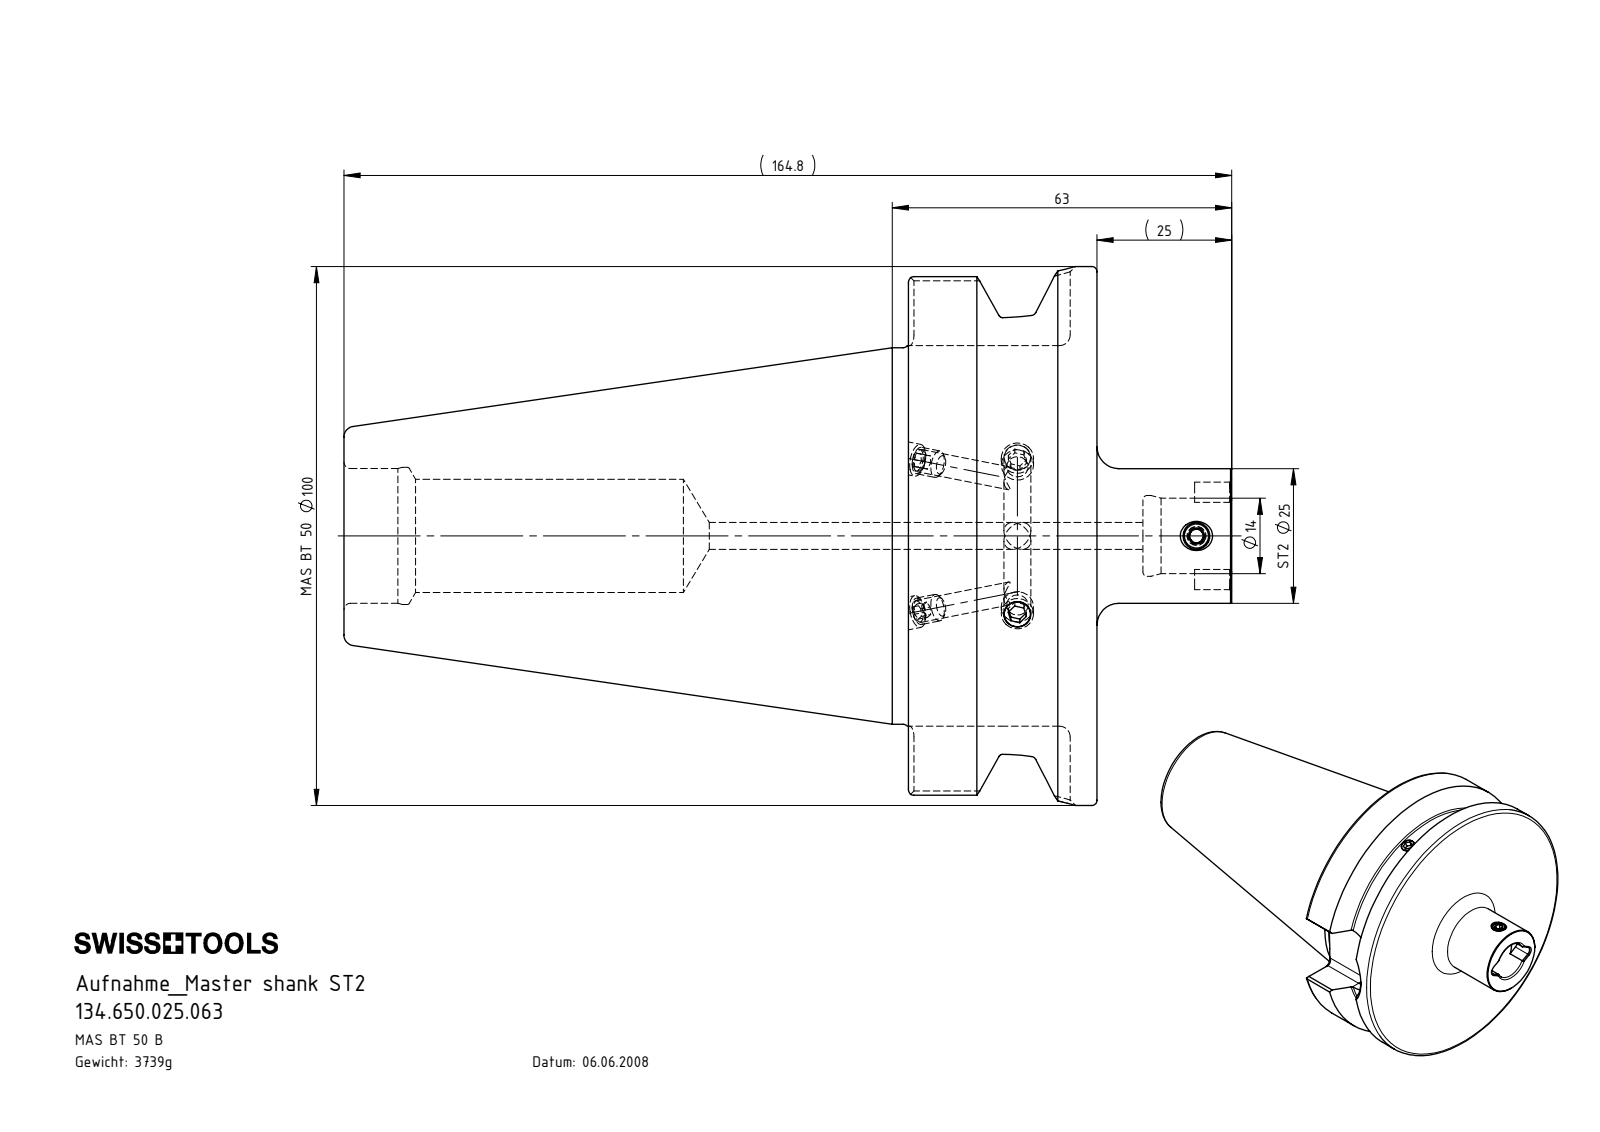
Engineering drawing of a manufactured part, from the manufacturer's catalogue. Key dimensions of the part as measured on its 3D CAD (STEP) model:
Part name (STEP PRODUCT): ST2-ER1.001.006_A; BB5-ST2.K01.063_A_mit Bundkhlung; ISO 4026 - M6 x 5; BB5-ST2.K01.063
STEP written by: SolidWorks 2015 (CONFIG_CONTROL_DESIGN)
Units: millimetres
Bodies: 3 solids, 170 faces (45 planar, 55 cylindrical, 70 other)
Overall size (bounding box): 164.8 × 100 × 100
Volume: 475 795 mm³ · Surface area: 54 662 mm²
Round holes (diameter × count): ⌀5 ×2, ⌀6 ×2, ⌀4.5 ×1, ⌀14 ×1, ⌀15 ×1, ⌀21 ×1, ⌀25 ×1, ⌀25.45 ×1
Round bosses / shafts (diameter × count): ⌀100 ×1, ⌀85 ×1, ⌀69.85 ×1, ⌀6 ×1, ⌀5 ×1
Partial cylindrical surfaces — rounded edges, fillets, slot ends (radius × count): R2 ×8, R1.8 ×2, R12.85 ×1
Main face-to-face distances: 35, 70.6, 104.8, 139.8, 25.7, 164.8, 60, 25, 148.3, 43.5
